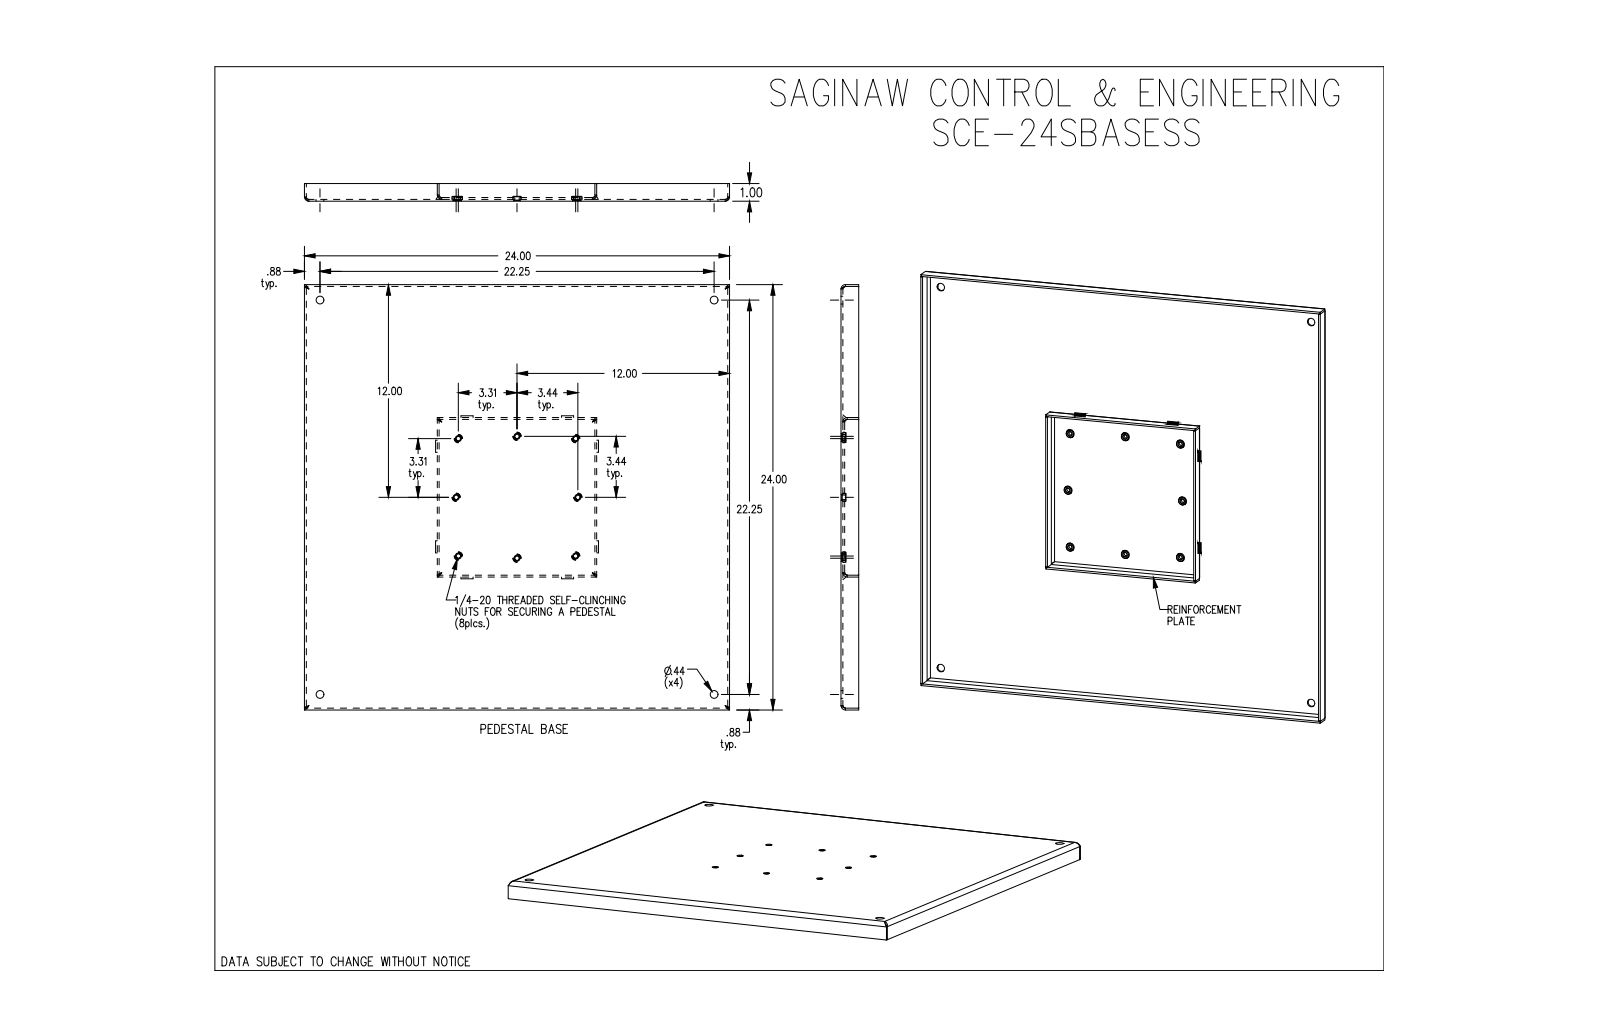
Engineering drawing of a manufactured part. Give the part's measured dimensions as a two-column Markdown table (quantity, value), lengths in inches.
| quantity | value |
| --- | --- |
| part name | SCE-24SBASE |
| STEP written by | SolidWorks 2021 (AUTOMOTIVE_DESIGN) |
| units | inches |
| bodies | 9 solids, 151 faces (35 planar, 68 cylindrical, 48 other) |
| overall size | 18 × 18 × 1 |
| volume | 70.48 in³ |
| surface area | 769.1 in² |
| round holes (diameter × count) | 0.25 × 8, 0.344 × 8, 0.438 × 4 |
| round bosses / shafts (diameter × count) | 0.44 × 8, 0.343 × 8 |
| partial cylindrical surfaces (radius × count) | 0.13 × 4, 0.318 × 4 |
| main face-to-face distances | 0.188, 17.812, 18, 17.624, 0.812, 1, 0.642, 0.17, 0.358, 0.899 |
| hole center spacings | 3.313, 3.315, 4.774, 7.407, 7.519, 9.381, 9.444, 12.409 |
